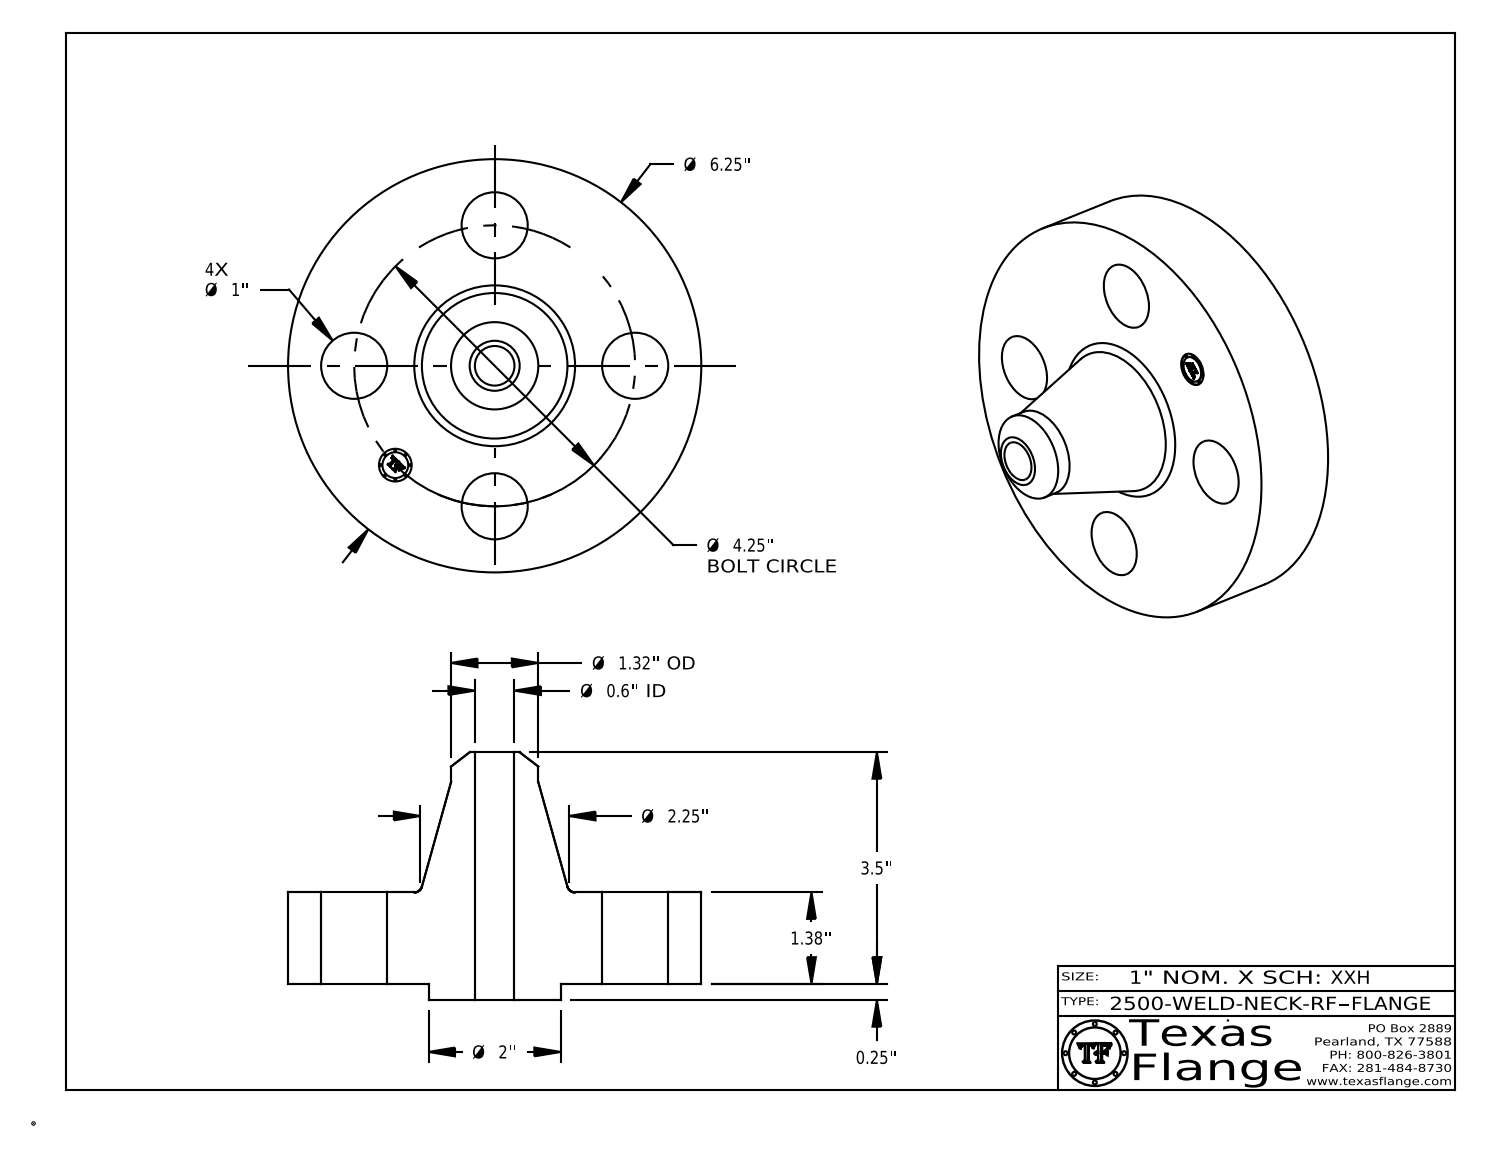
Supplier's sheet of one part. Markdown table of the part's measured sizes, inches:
| quantity | value |
| --- | --- |
| part name | 2500-WELD-NECK-RF |
| STEP written by | CATIA V5 STEP AP214 (AUTOMOTIVE_DESIGN) |
| units | inches |
| bodies | 1 solid, 411 faces (369 planar, 36 cylindrical, 6 other) |
| overall size | 6.25 × 6.25 × 3.75 |
| volume | 42.52 in³ |
| surface area | 115.8 in² |
| round holes (diameter × count) | 1 × 4, 0.495 × 1, 0.599 × 1 |
| round bosses / shafts (diameter × count) | 0.03 × 8, 6.25 × 1, 2 × 1, 1.32 × 1, 0.39 × 1 |
| main face-to-face distances | 1.38, 0.25, 1.63, 3.75, 3.5, 2.12, 1.615, 1.365, 0.015, 2.135 |
| hole center spacings | 2.125, 3.006, 1.626, 3.927, 4.25 |
